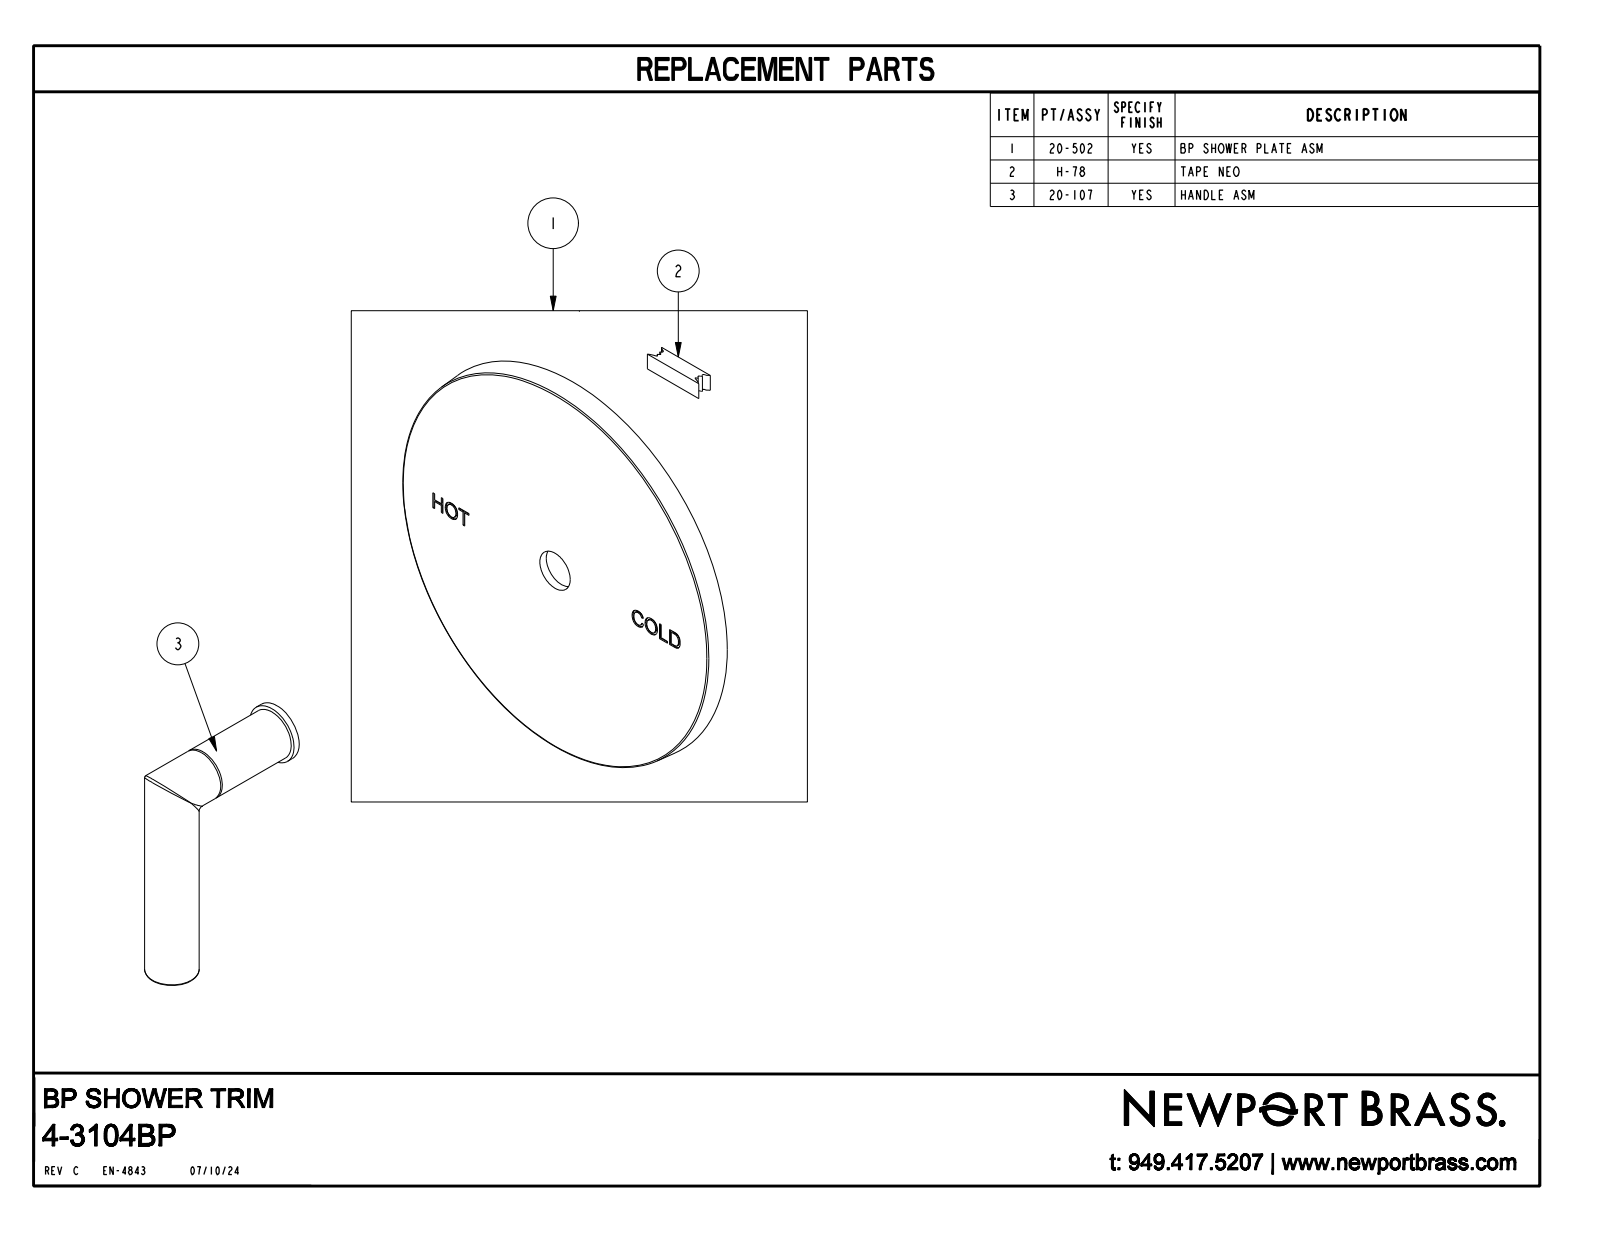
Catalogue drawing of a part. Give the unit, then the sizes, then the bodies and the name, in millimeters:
Units: millimetres
Overall size (bounding box): 152.4 × 152.4 × 71.2
Round bosses / shafts (diameter × count): ⌀19.1 ×2, ⌀21.8 ×1, ⌀12.9 ×1
Main face-to-face distances: 8.9, 0.8, 37.4, 46.3, 47, 38.2, 9.7, 12.2, 3.3, 2.5
Volume: 197 300 mm³ · Surface area: 48 570 mm²
Bodies: 1 solid, 149 faces (51 planar, 12 cylindrical, 86 other)
Part name (STEP PRODUCT): 4-3104BP
STEP written by: CREO PARAMETRIC BY PTC INC, 2018400 (CONFIG_CONTROL_DESIGN)
